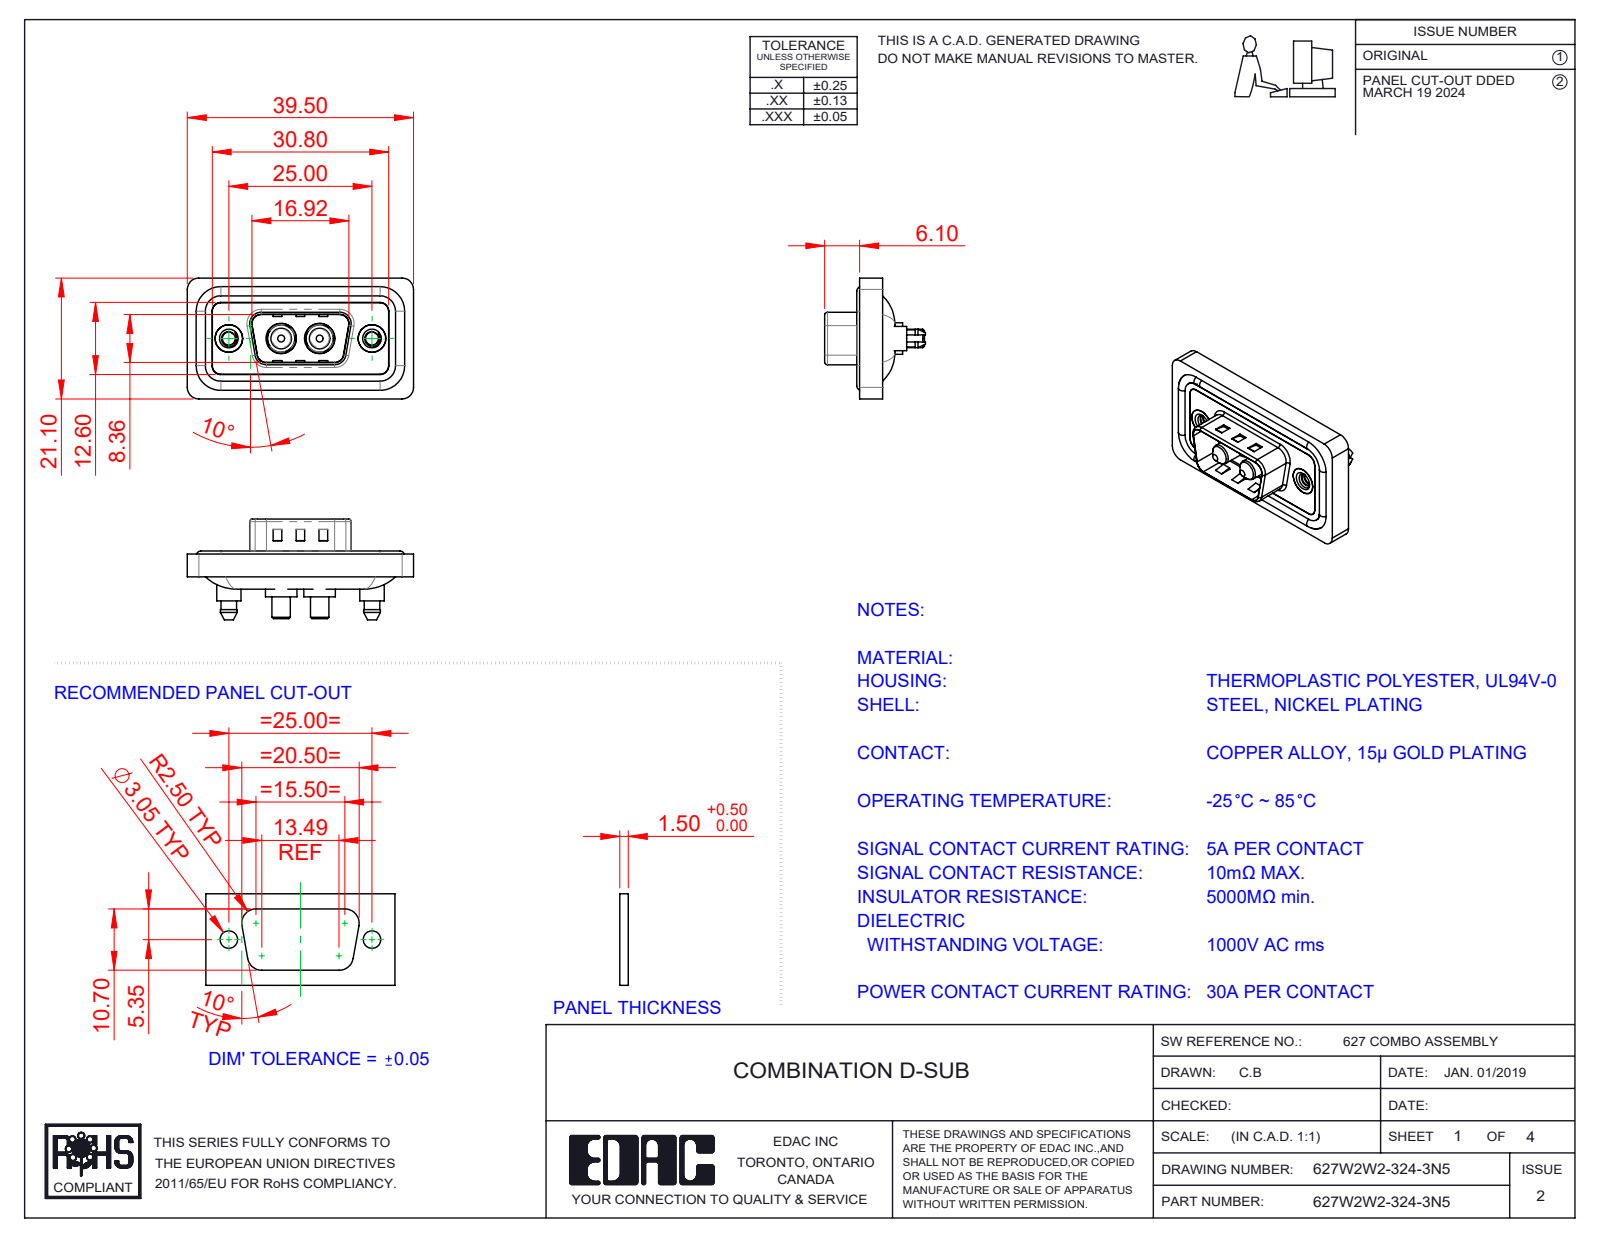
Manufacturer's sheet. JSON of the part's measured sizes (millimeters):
{"part_name": "Power Pin_30A S; 627Combo Waterproof Housing_09 Contacts; 627W2W2-324-3N5; 627Combo Shell Rear_09 Contacts (+3 more)", "step_written_by": "SolidWorks 2023 (CONFIG_CONTROL_DESIGN)", "units": "millimeters", "bodies": {"solids": 11, "faces": 539, "planar": 181, "cylindrical": 250, "other": 108}, "overall_size": [39.5, 21.1, 17.6], "volume_mm3": 4608, "surface_area_mm2": 7326, "round_holes": [[2.26, 2], [4, 2], [4.8, 2], [4.85, 2], [5, 2], [5.3, 2]], "round_bosses_or_shafts": [[1.6, 4], [5.5, 2], [5.4, 2], [5.2, 2], [4.9, 2], [4.75, 2], [4.25, 2], [3.75, 2]], "partial_cylinders_radius": [[1.5, 24], [2, 18], [1.6, 10], [0.5, 8], [0.25, 4], [0.6, 4], [0.65, 4], [0.9, 4]], "face_to_face_distances": [0.4, 1.1, 2.9, 3.1, 0.5, 1.6, 1.5, 4, 0.7, 2.5], "hole_center_spacings": [9.14, 15.86, 6.72, 25]}
